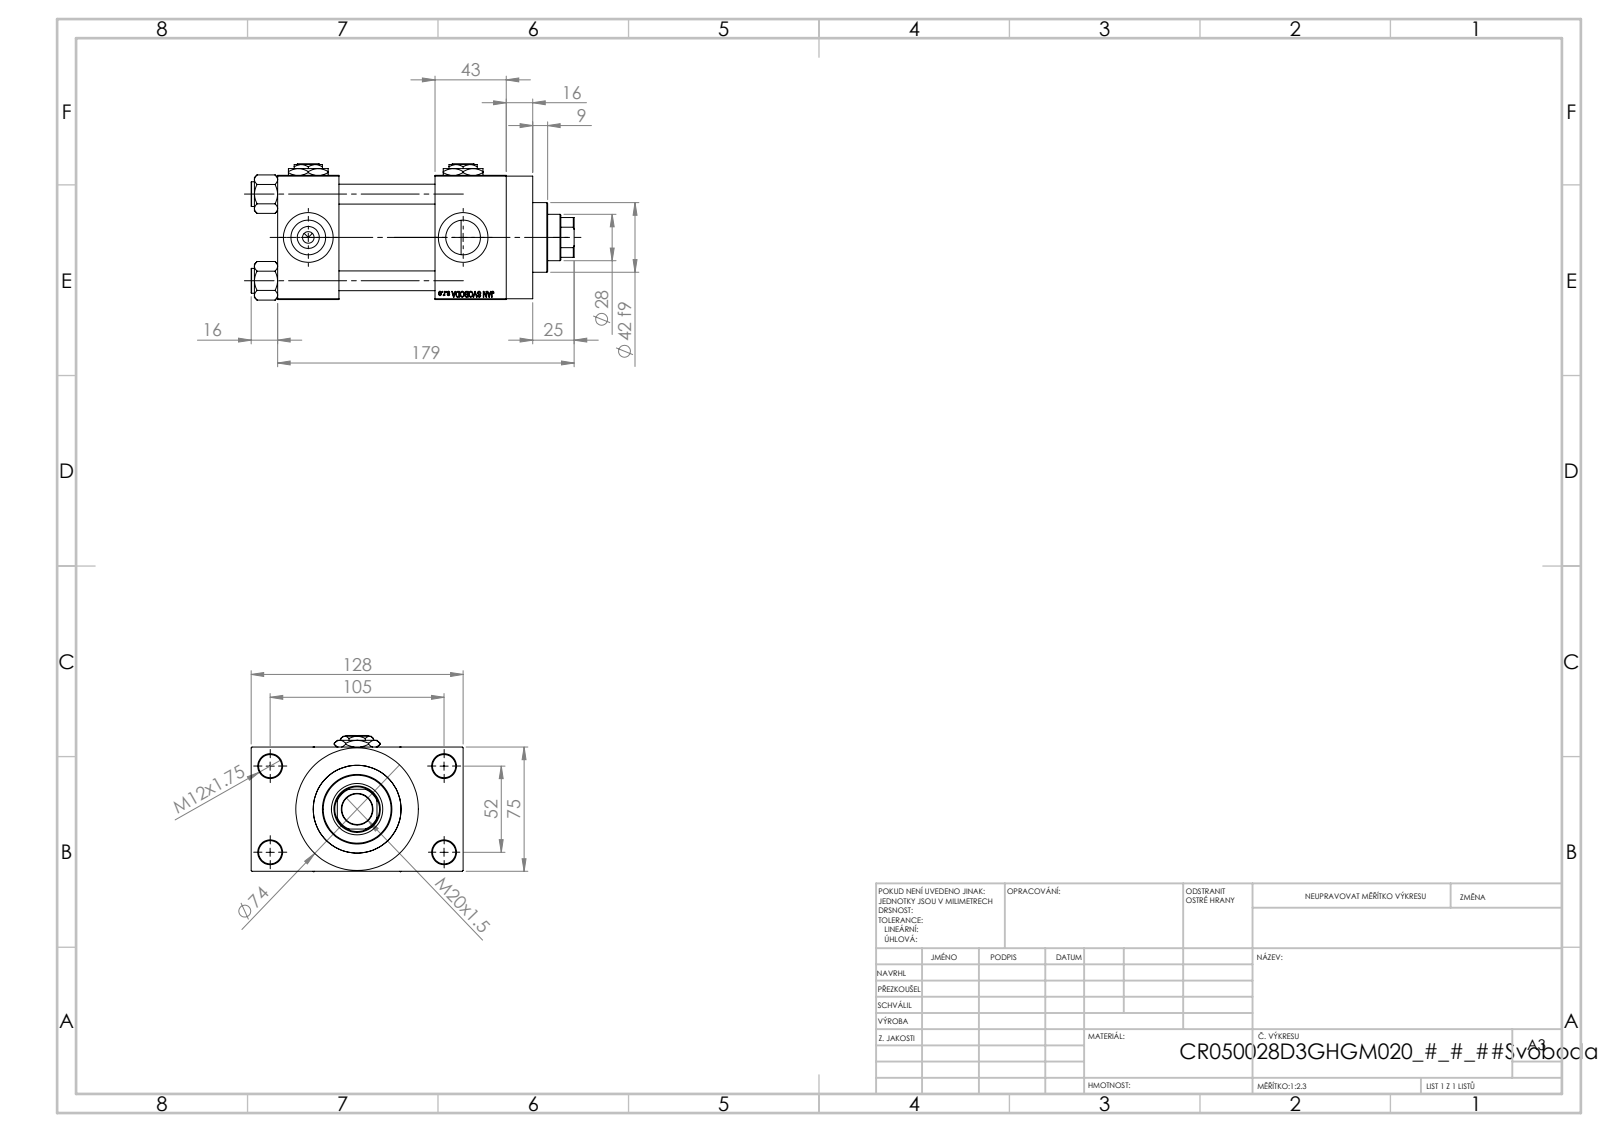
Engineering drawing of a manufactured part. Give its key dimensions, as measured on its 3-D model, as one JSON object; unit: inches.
{"part_name": "Zatka_pro_OIL_PORT; V215CR_D_Body; V215CR_VCP_D; V215_VC_A (+2 more)", "step_written_by": "SolidWorks 2019 (CONFIG_CONTROL_DESIGN)", "units": "inches", "bodies": {"solids": 13, "faces": 1204, "planar": 545, "cylindrical": 99, "other": 560}, "overall_size": [7.677, 5.039, 3.239], "volume_in3": 48.93, "surface_area_in2": 271, "round_holes": [[0.472, 4], [0.551, 4], [0.825, 4], [1.181, 4], [0.276, 3], [0.728, 1], [1.102, 1], [1.22, 1], [1.614, 1], [1.969, 1], [2.087, 1]], "round_bosses_or_shafts": [[0.591, 4], [2.913, 1], [2.205, 1], [1.654, 1]], "partial_cylinders_radius": [[0.531, 1]], "face_to_face_distances": [2.953, 2.283, 1.457, 3.74, 1.043, 5.433, 3.976, 1.693, 3.996, 0.63], "hole_center_spacings": [1.037, 1.456, 2.059, 2.3, 2.307, 3.096, 3.715, 2.047]}
